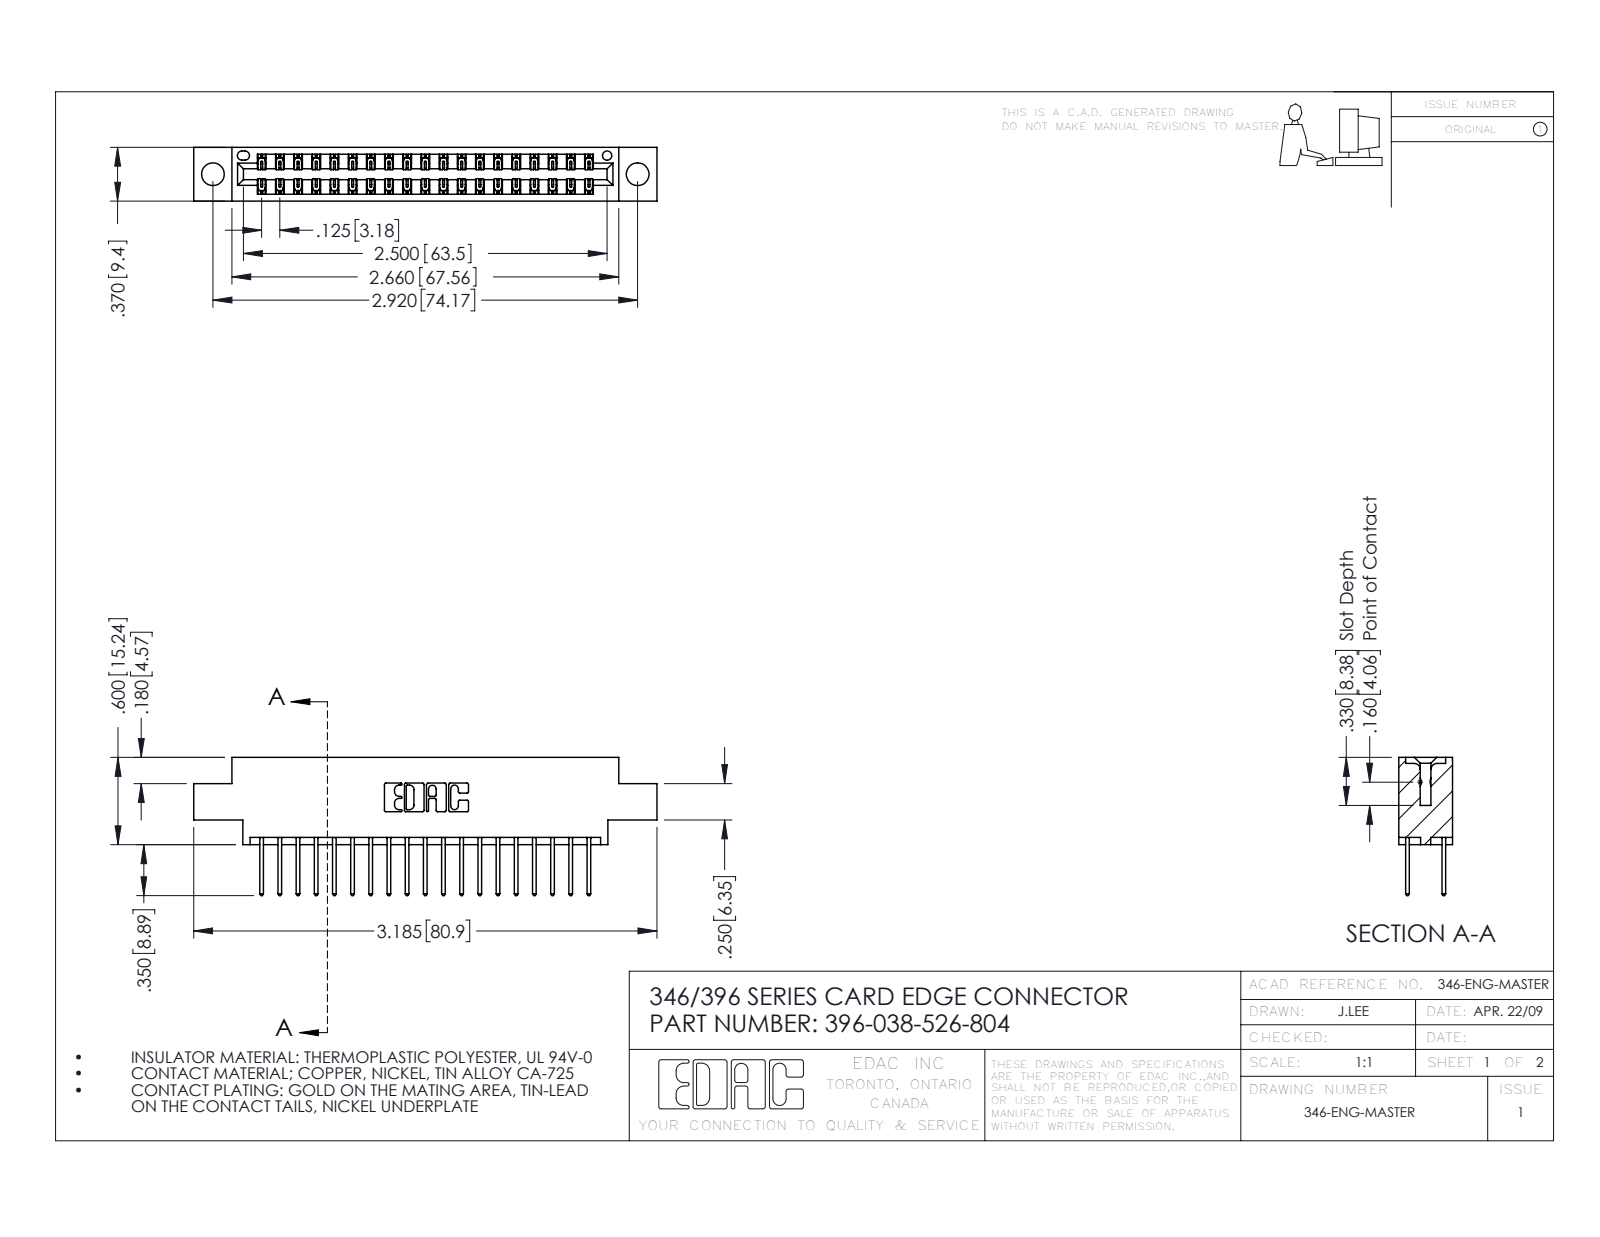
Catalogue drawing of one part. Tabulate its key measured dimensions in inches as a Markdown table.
| quantity | value |
| --- | --- |
| part name | 346 Part_0.170 Offset - 0.156 Dia-TH; 396-038-526-804; 345-292-001_345-293-126 |
| STEP written by | SolidWorks 2016 (CONFIG_CONTROL_DESIGN) |
| units | inches |
| bodies | 39 solids, 2102 faces (1410 planar, 692 cylindrical, 0 other) |
| overall size | 3.185 × 0.95 × 0.37 |
| volume | 0.46 in³ |
| surface area | 15.9 in² |
| round holes (diameter × count) | 0.156 × 2, 0.064 × 1 |
| partial cylindrical surfaces (radius × count) | 0.006 × 57, 0.01 × 38, 0.01 × 22, 0.007 × 6, 0.031 × 6, 0.026 × 3, 0.014 × 2, 0.022 × 2 |
| main face-to-face distances | 0.048, 0.322, 0.25, 0.37, 0.072, 0.298, 0.025, 0.275, 0.148, 0.222 |
| hole center spacings | 0.246, 2.713, 2.92 |
